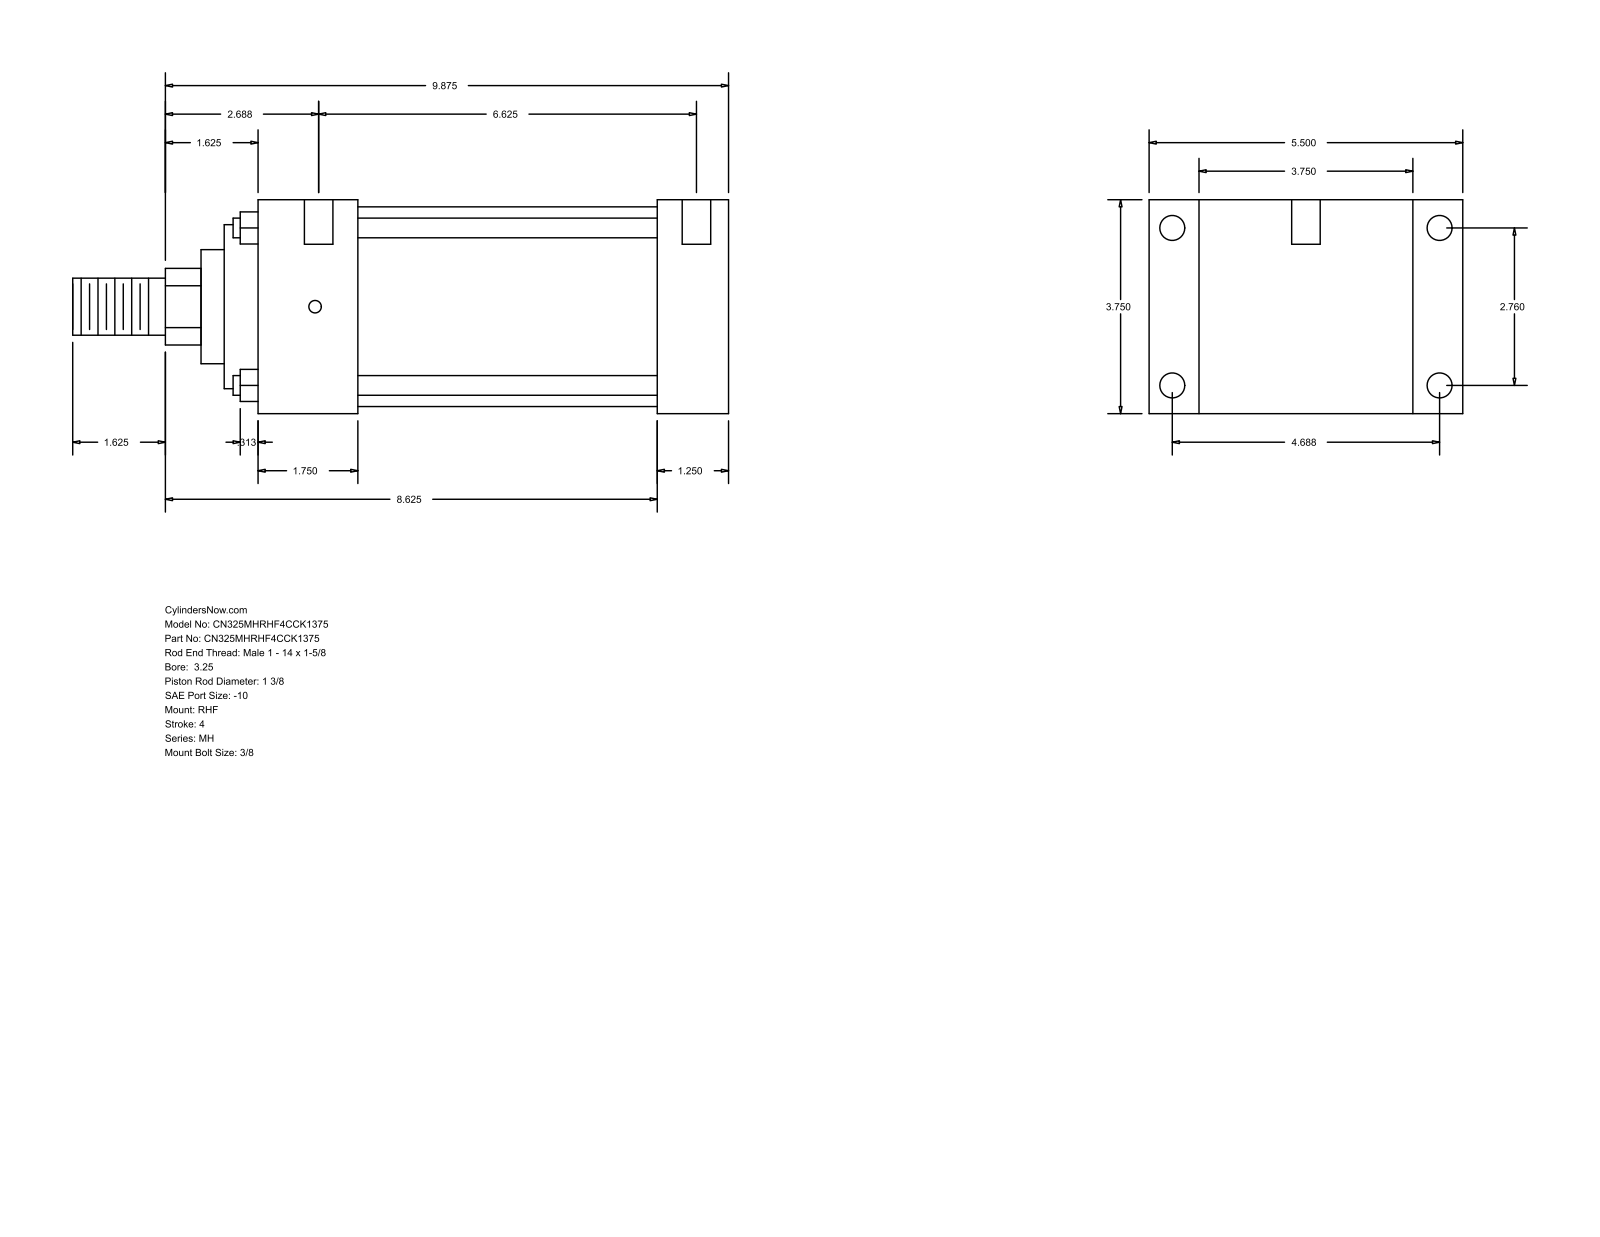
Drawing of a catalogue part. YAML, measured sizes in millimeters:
part_name: "MH_RHF__0325_1.375"
step_written_by: "GSSL Pune (CONFIG_CONTROL_DESIGN)"
units: millimeters
bodies: {solids: 0, faces: 90, planar: 61, cylindrical: 29, other: 0}
overall_size: [292.1, 139.7, 95.25]
round_holes:
  - {diameter: 5.56, count: 4}
  - {diameter: 11.13, count: 4}
  - {diameter: 12.7, count: 2}
round_bosses_or_shafts:
  - {diameter: 8.76, count: 4}
  - {diameter: 88.9, count: 1}
  - {diameter: 73.03, count: 1}
  - {diameter: 50.8, count: 1}
  - {diameter: 34.92, count: 1}
  - {diameter: 25.4, count: 1}
partial_cylinders:
  - {radius: 17.06, count: 1}
face_to_face_distances: [95.24, 31.75, 22.23, 117.47, 177.8, 209.55, 139.7, 44.45, 133.35, 165.1]
hole_center_spacings: [70.1, 119.06, 138.16, 174.63, 1.59, 4.76, 168.28, 169.87]
